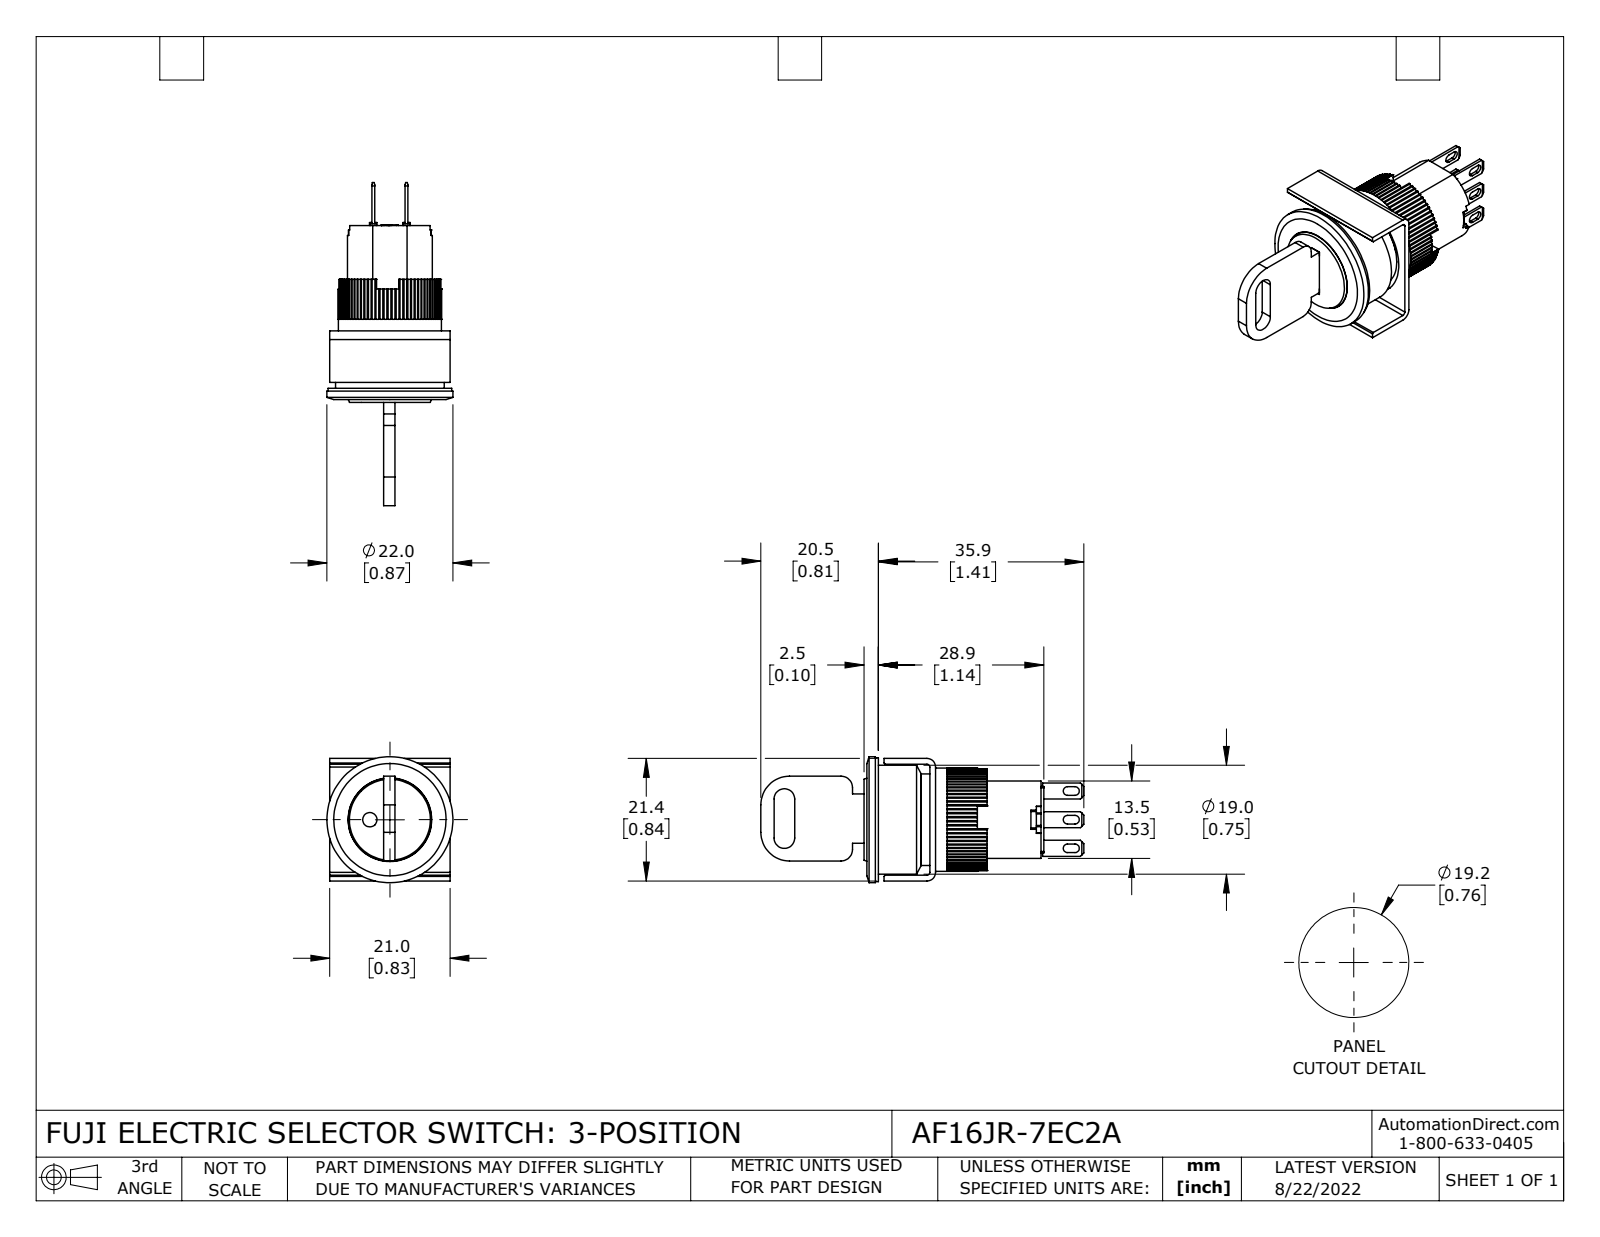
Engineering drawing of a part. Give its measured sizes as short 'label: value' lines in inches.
name: AF16JR-7EC2A
written by: SolidWorks 2021 (CONFIG_CONTROL_DESIGN)
unit: in
bodies: 13 solids, 707 faces (518 planar, 183 cylindrical, 6 other)
size: 2.22 × 0.866 × 0.866
volume: 0.495 in³; area: 11.24 in²
holes: 1× ⌀0.039, 1× ⌀0.098, 1× ⌀0.575, 1× ⌀0.709, 1× ⌀0.748
bosses: 1× ⌀0.866, 1× ⌀0.85, 1× ⌀0.63, 1× ⌀0.583, 1× ⌀0.571
rounds: 80× R0.01, 12× R0.008, 6× R0.03, 2× R0.02, 2× R0.059, 2× R0.071, 2× R0.079, 2× R0.197
face distances: 0.079, 0.039, 0.02, 0.374, 0.177, 0.098, 0.394, 0.803, 0.059, 0.764
hole spacings: 0.138
